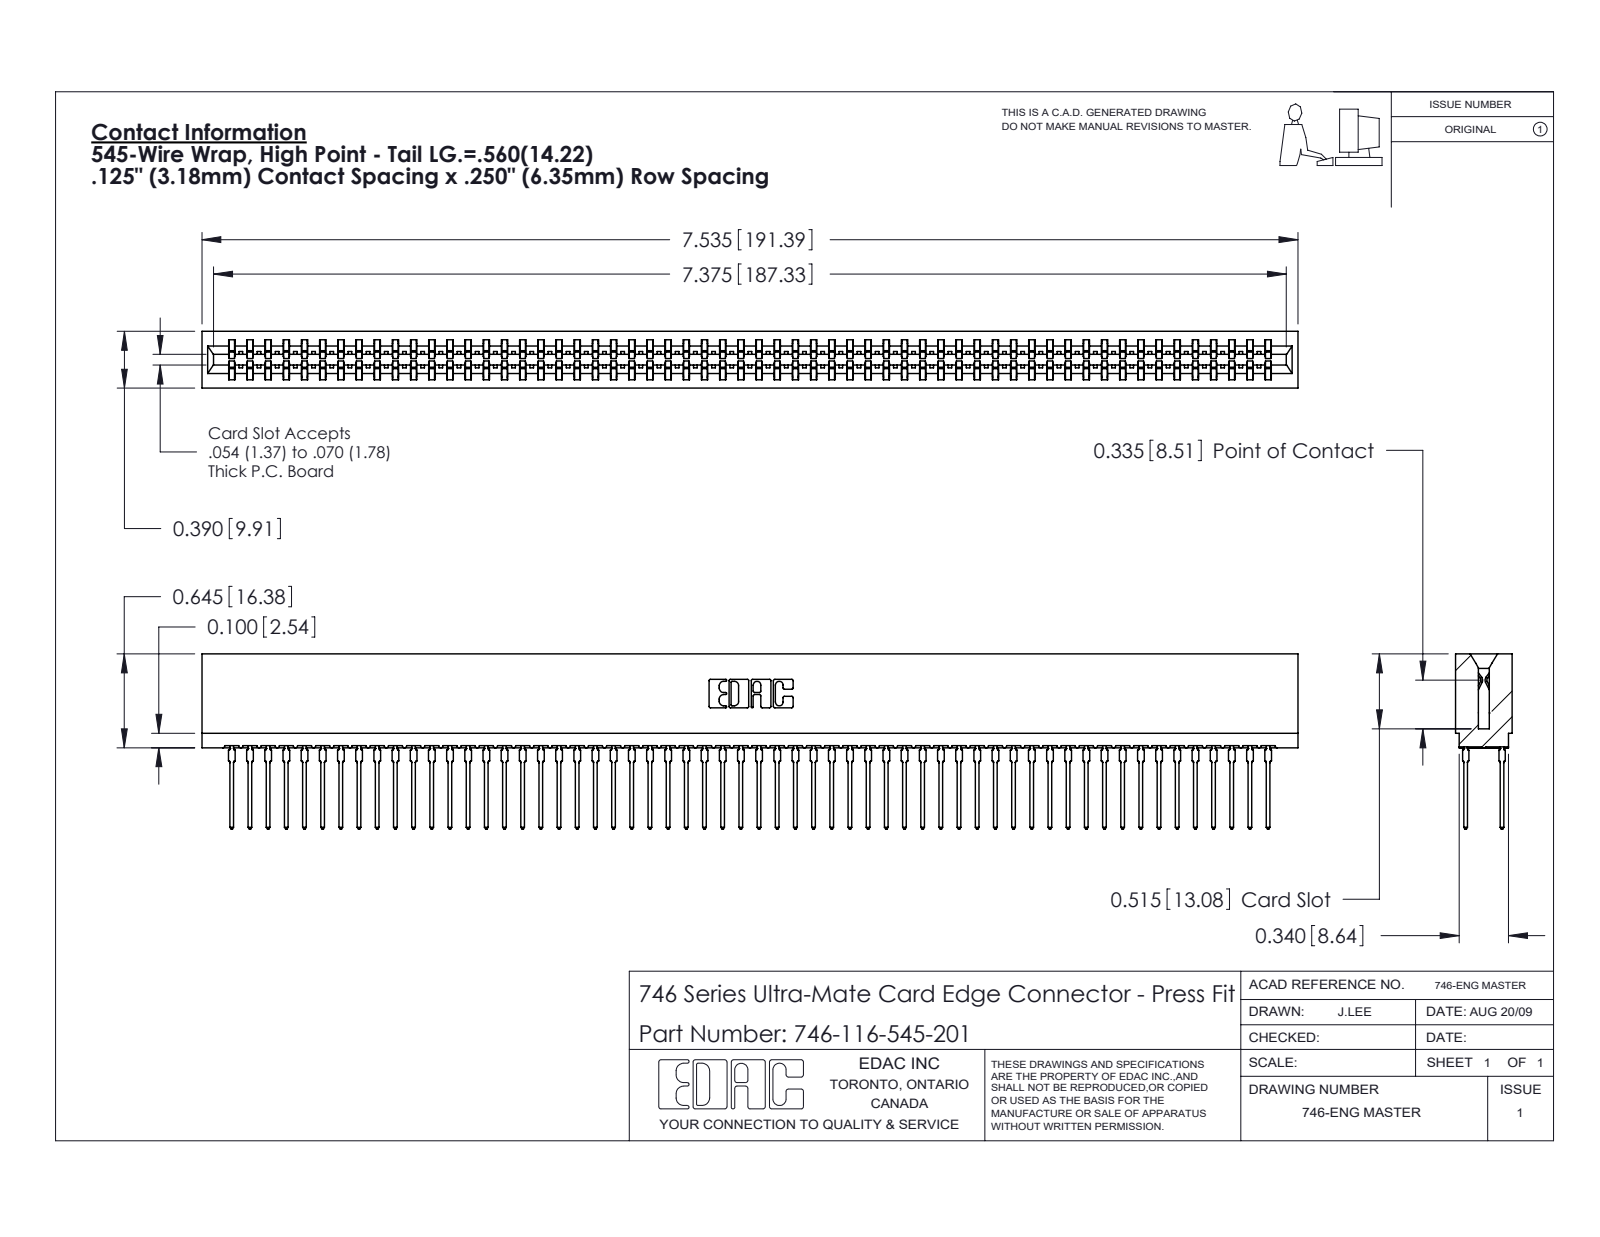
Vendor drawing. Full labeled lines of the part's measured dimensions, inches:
Part name (STEP PRODUCT): 746-292-001_545; 746 Part_.515 Slot Depth - 01; 746-116-545-201
STEP written by: SolidWorks 2020 (CONFIG_CONTROL_DESIGN)
Units: inches
Bodies: 117 solids, 10479 faces (5391 planar, 2072 cylindrical, 3016 other)
Overall size (bounding box): 7.535 × 1.204 × 0.39
Volume: 1.27 in³ · Surface area: 55.17 in²
Partial cylindrical surfaces — rounded edges, fillets, slot ends (radius × count): R0.021 ×232, R0.015 ×59, R0.01 ×22, R0.005 ×8, R0.011 ×8, R0.007 ×6, R0.031 ×6, R0.026 ×3
Main face-to-face distances: 0.057, 0.333, 0.25, 0.39, 0.025, 0.307, 0.275, 0.083, 0.174, 0.158
